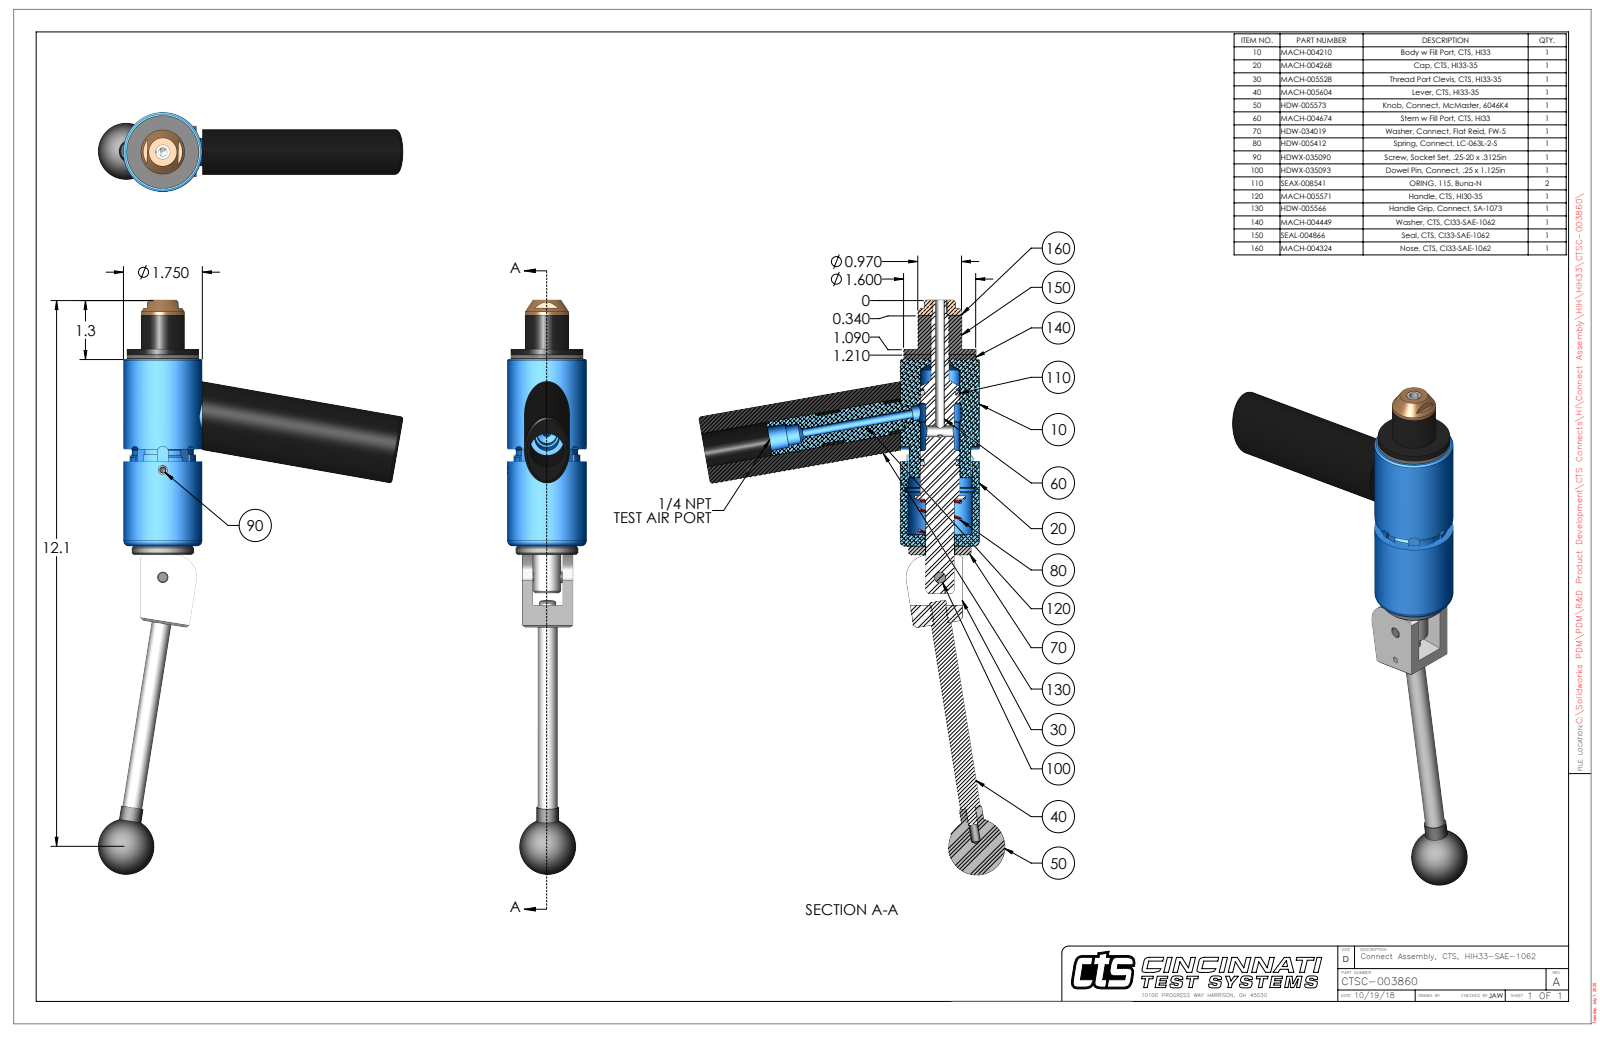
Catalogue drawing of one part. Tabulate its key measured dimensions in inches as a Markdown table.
| quantity | value |
| --- | --- |
| part name | CTSC-003860 |
| STEP written by | SolidWorks 2023 (AUTOMOTIVE_DESIGN) |
| units | inches |
| bodies | 10 solids, 327 faces (117 planar, 140 cylindrical, 70 other) |
| overall size | 12.729 × 6.763 × 1.75 |
| volume | 18.43 in³ |
| surface area | 116.9 in² |
| round holes (diameter × count) | 0.201 × 2, 0.313 × 2, 0.15 × 1, 0.187 × 1, 0.204 × 1, 0.249 × 1, 0.25 × 1, 0.251 × 1, 0.39 × 1, 0.397 × 1, 0.403 × 1, 0.438 × 1 |
| round bosses / shafts (diameter × count) | 0.312 × 2, 0.25 × 2, 1.75 × 1, 1.6 × 1, 1.38 × 1, 0.97 × 1, 0.75 × 1, 0.625 × 1 |
| partial cylindrical surfaces (radius × count) | 0.125 × 4, 0.029 × 2, 0.15 × 1, 0.166 × 1, 0.166 × 1, 0.33 × 1, 0.5 × 1, 0.695 × 1 |
| main face-to-face distances | 0.098, 4.244, 4.146, 1.12, 0.12, 4.432, 4.334, 0.188, 0.75, 0.87 |
| hole center spacings | 0.74, 2.376, 3.116 |
